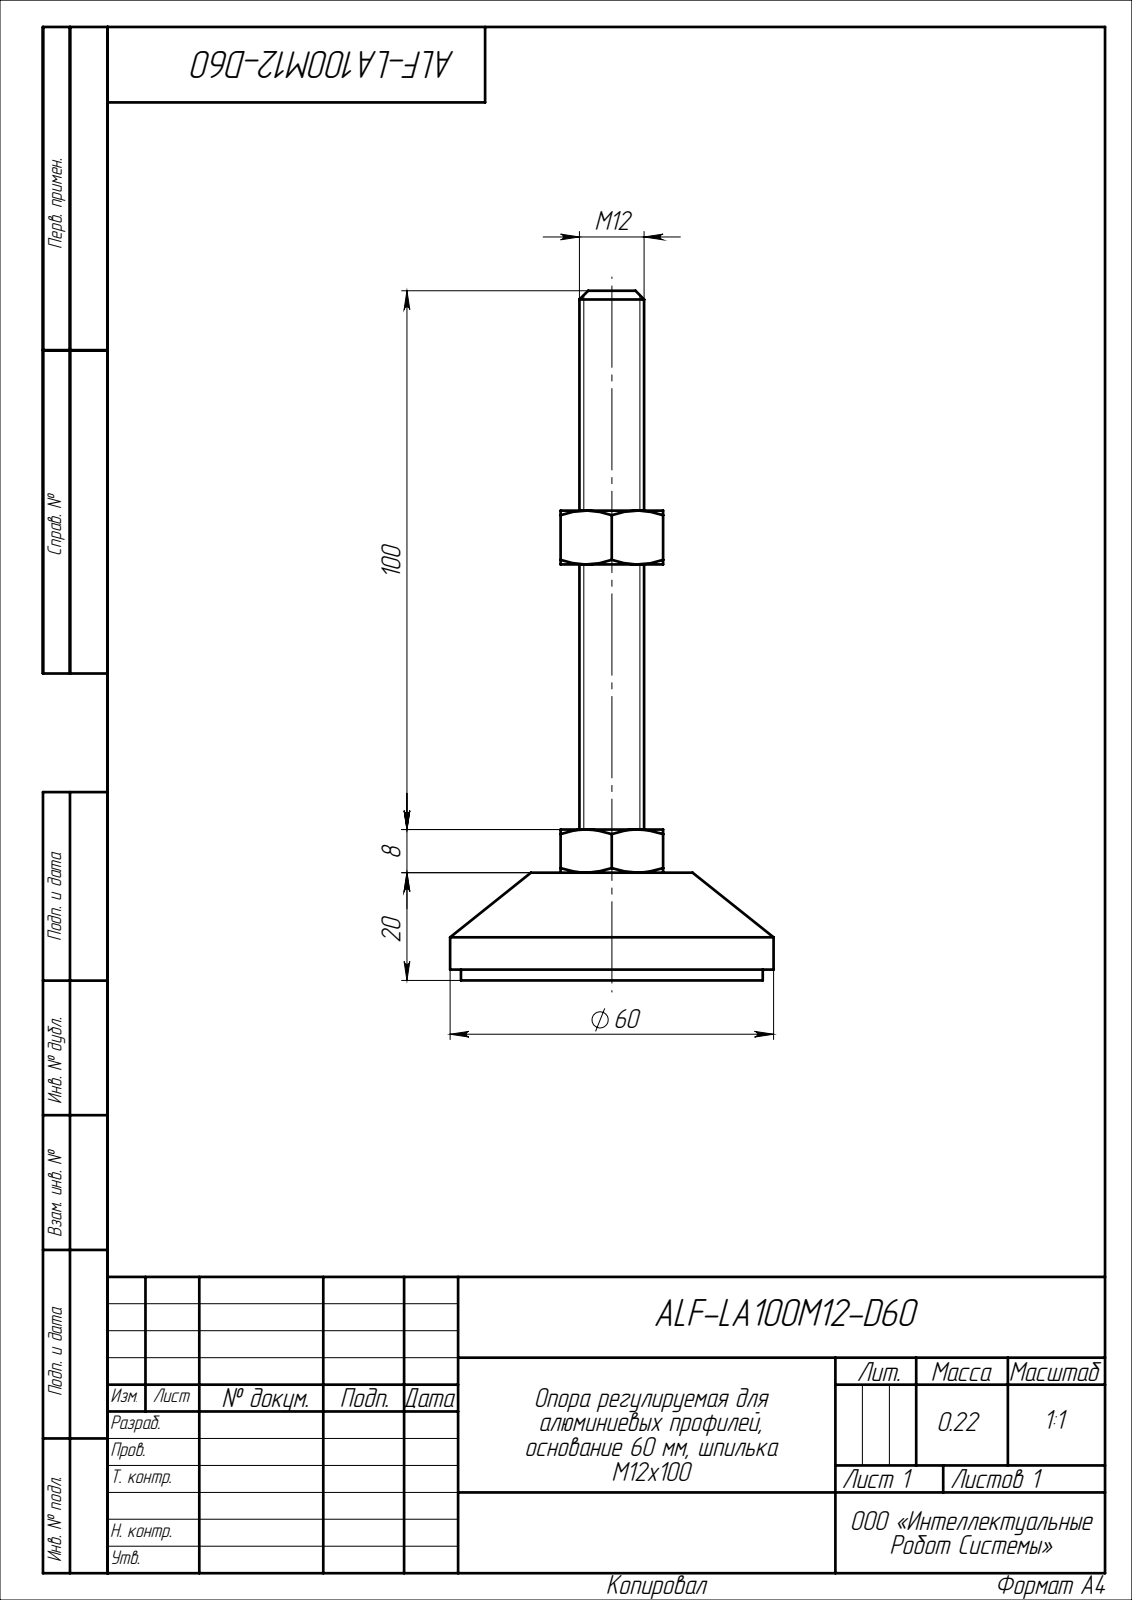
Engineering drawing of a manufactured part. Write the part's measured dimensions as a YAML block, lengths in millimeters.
part_name: "ALF-LA100M12-D60"
step_written_by: "SolidWorks 2022 (CONFIG_CONTROL_DESIGN)"
units: millimeters
bodies: {solids: 1, faces: 55, planar: 19, cylindrical: 8, other: 28}
overall_size: [128, 60, 60]
volume: 57415
surface_area: 12670
round_bosses_or_shafts:
  - {diameter: 60, count: 1}
  - {diameter: 56, count: 1}
  - {diameter: 12, count: 1}
face_to_face_distances: [19, 20, 2, 18, 28, 26, 8, 77.2, 75.2, 57.2]
